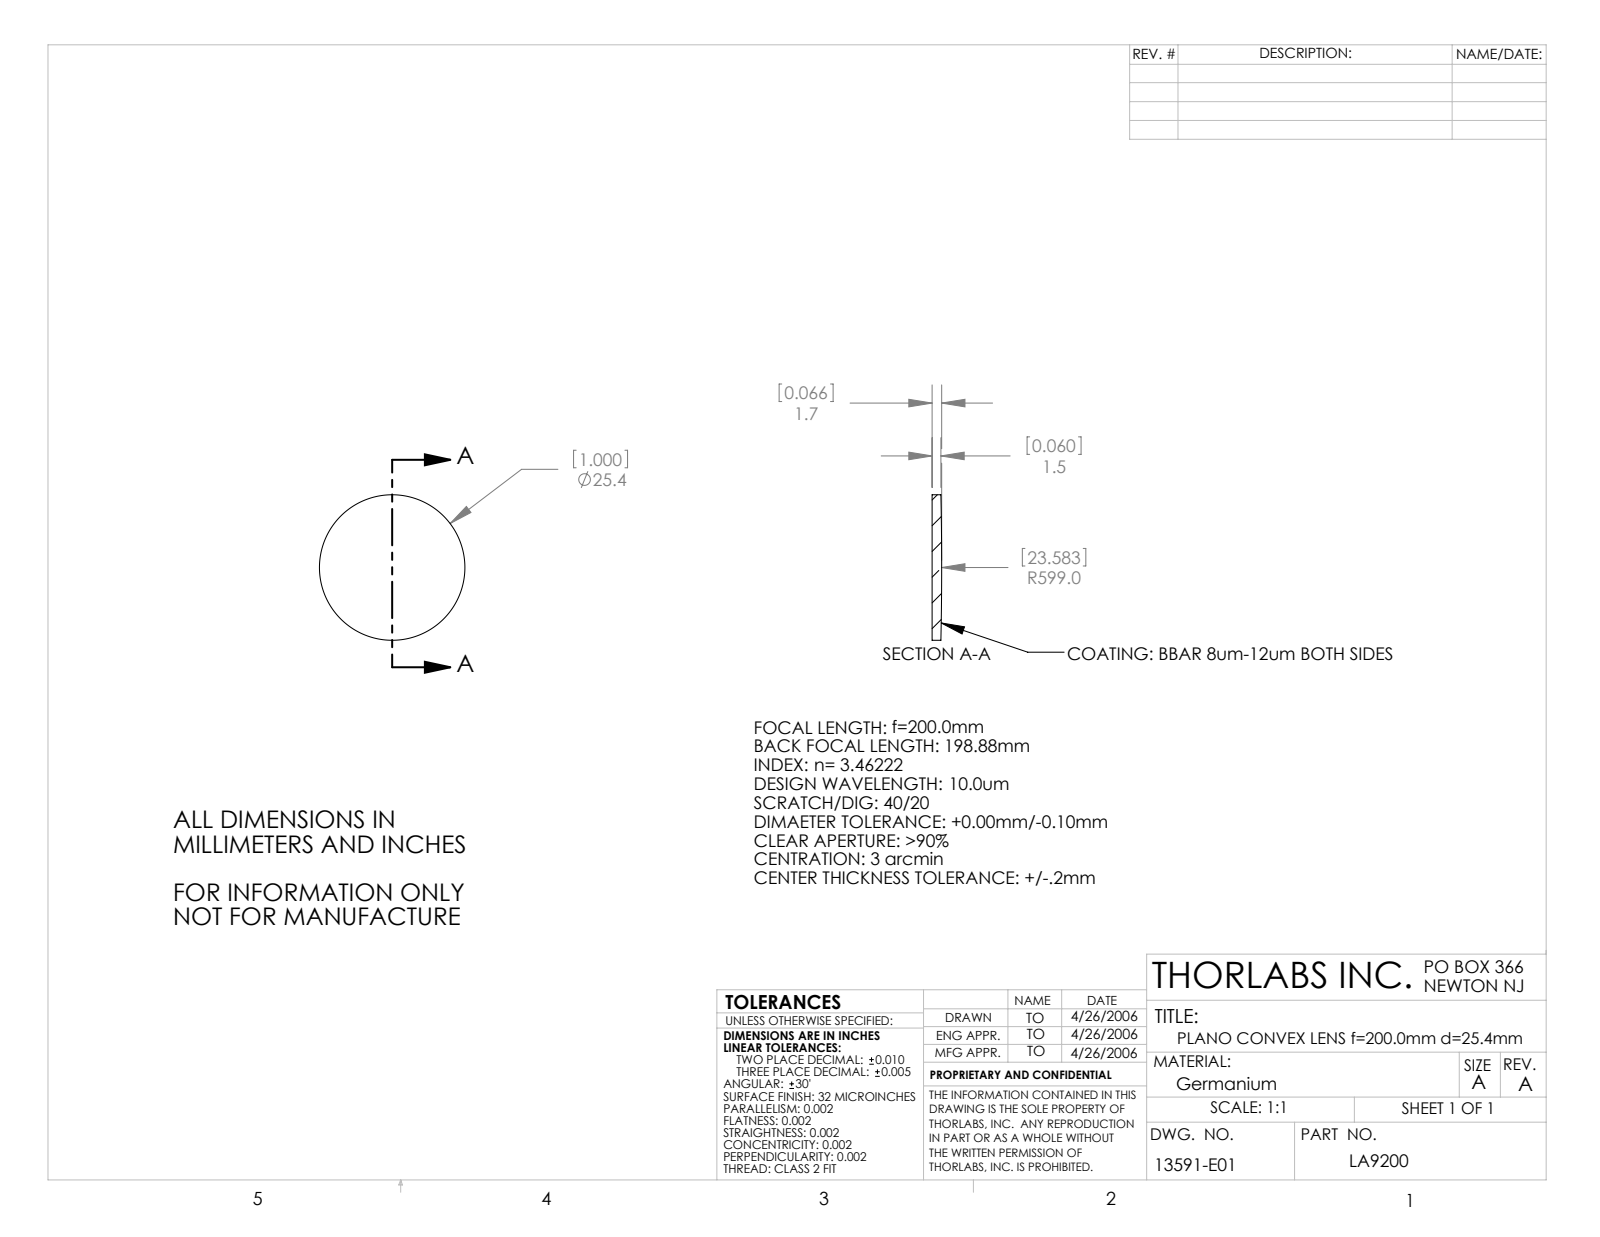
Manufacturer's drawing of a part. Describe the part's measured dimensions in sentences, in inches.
The part is named "13591-E0W". Its 3-D file was written by "SolidWorks 2007 (AUTOMOTIVE_DESIGN)". It is 0 solids with 5 faces: 1 planar, 2 cylindrical and 2 other. Overall it measures 1 by 1 by 0.066 inches. Round bosses or shafts: 1 of diameter 1.
